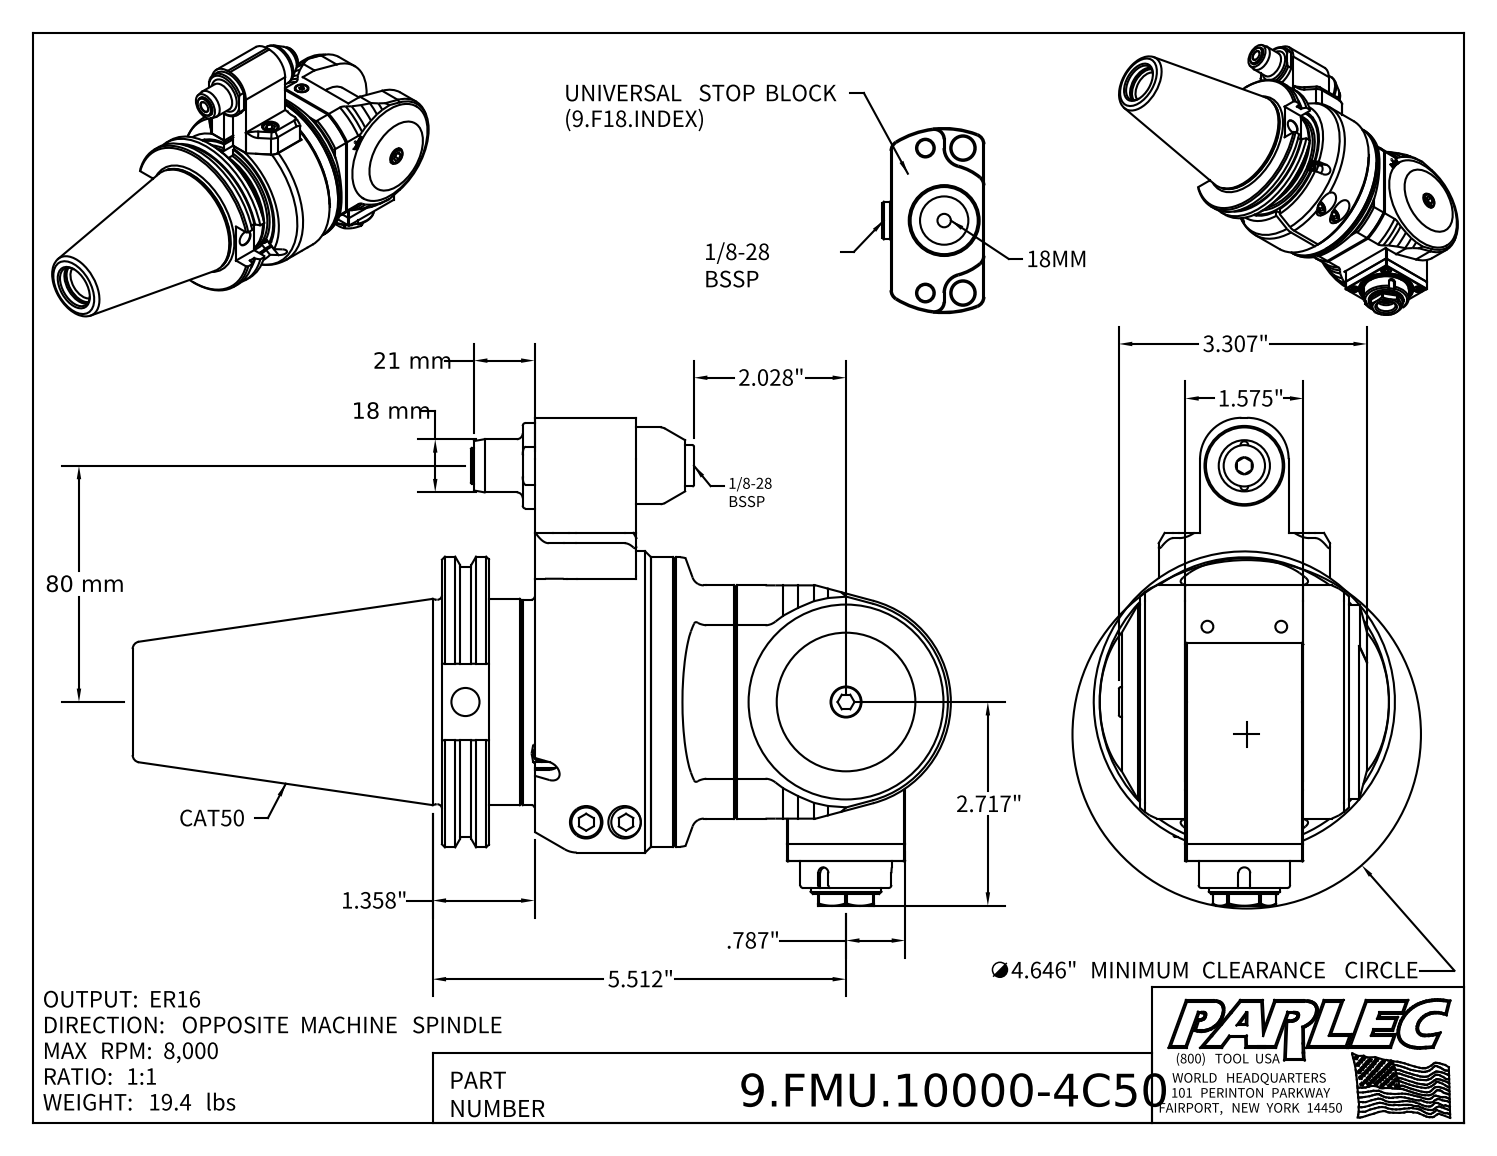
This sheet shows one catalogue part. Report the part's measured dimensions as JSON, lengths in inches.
{"part_name": "9.FMU.10000-4C50; 9_FMU_10000; 9_GA1_458_2 (Type 1, Cat50, 80mm)", "step_written_by": "Autodesk Inventor 2022 (AUTOMOTIVE_DESIGN)", "units": "inches", "bodies": {"solids": 6, "faces": 661, "planar": 337, "cylindrical": 145, "other": 179}, "overall_size": [10.909, 6.506, 4.016], "volume_in3": 79.56, "surface_area_in2": 297.2, "round_holes": [[0.276, 5], [0.413, 3], [0.433, 3], [0.102, 2], [0.157, 2], [0.197, 2], [0.335, 2], [0.409, 2], [0.098, 1], [0.118, 1], [0.256, 1], [0.375, 1]], "round_bosses_or_shafts": [[0.394, 7], [0.236, 6], [0.315, 3], [0.709, 2], [0.098, 2], [4.016, 1], [3.875, 1], [3.858, 1]], "partial_cylinders_radius": [[0.079, 11], [0.157, 6], [0.02, 2], [0.039, 2], [0.138, 2], [0.197, 2], [0.551, 2], [0.423, 1]], "face_to_face_distances": [0.531, 2.106, 1.26, 1.575, 0.61, 2.185, 2.717, 0.079, 3.031, 0.846], "hole_center_spacings": [0.886, 1.253, 0.276, 0.394, 0.872, 0.9, 1.118, 1.772]}
